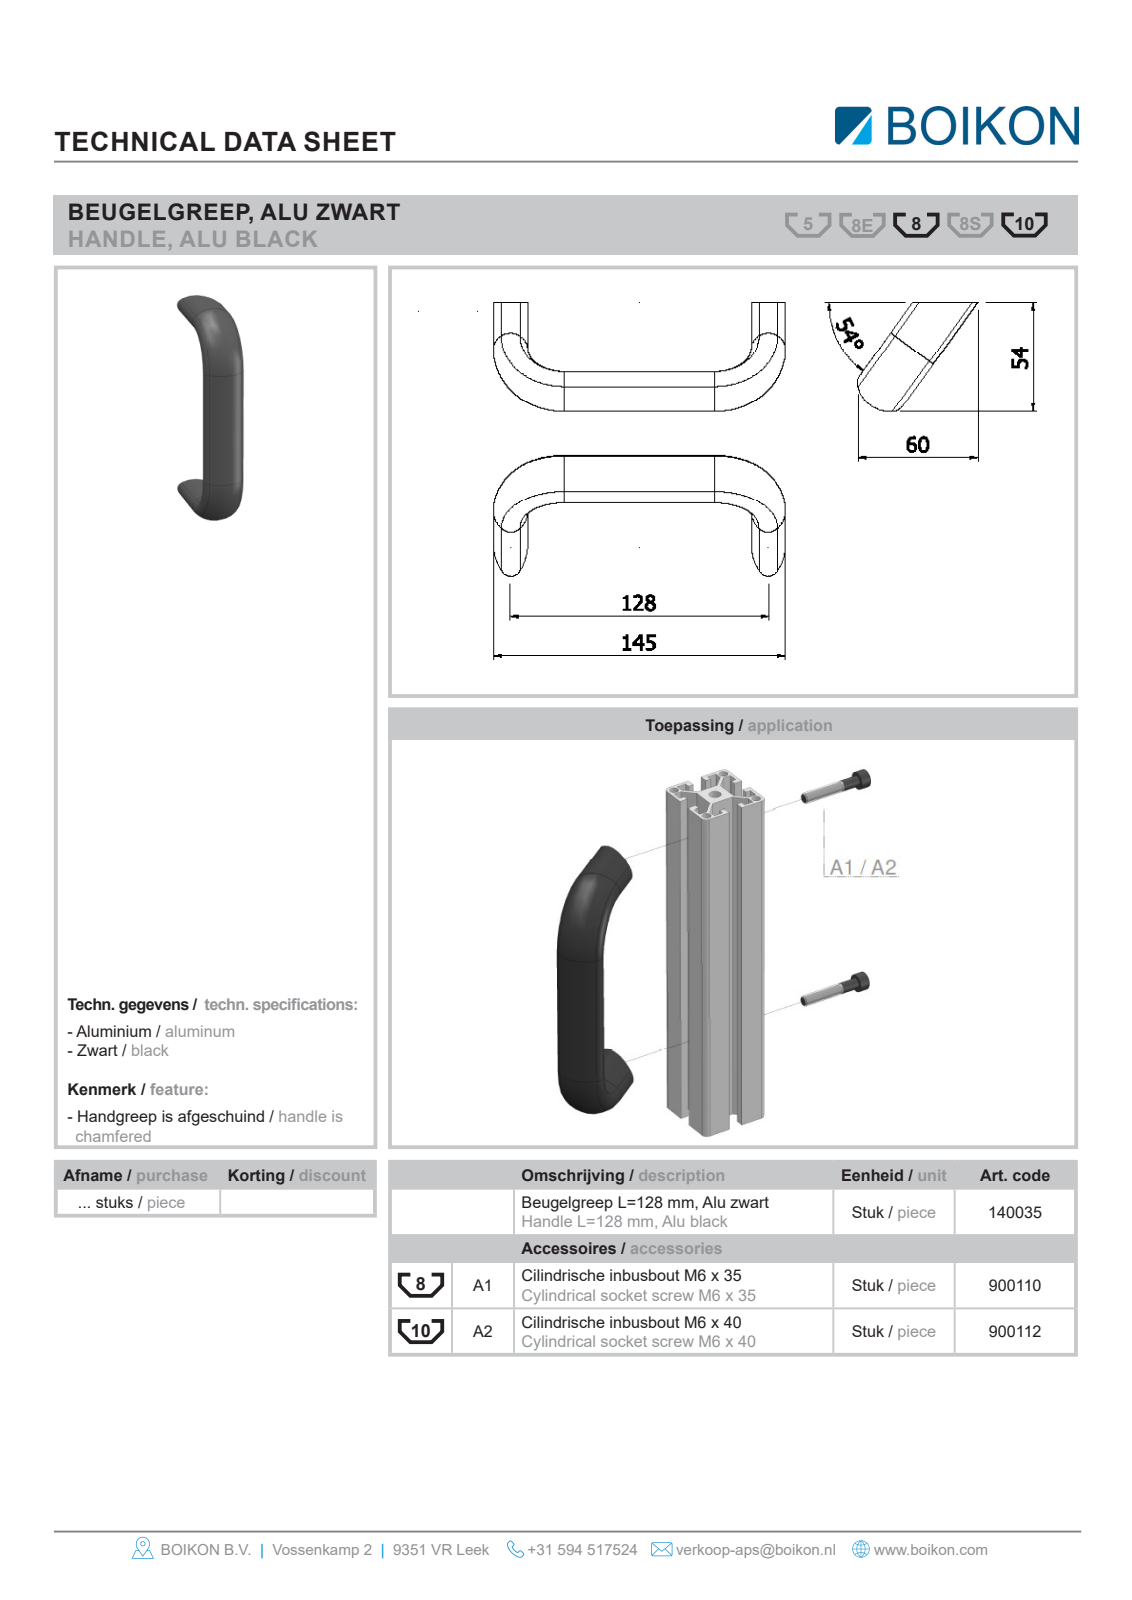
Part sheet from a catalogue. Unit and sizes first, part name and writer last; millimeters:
Units: millimetres
Overall size (bounding box): 145.01 × 87.64 × 59.9
Round holes (diameter × count): ⌀6.65 ×1, ⌀6.65 ×1
Round bosses / shafts (diameter × count): ⌀10 ×2, ⌀6 ×2, ⌀4.77 ×2
Partial cylindrical surfaces — rounded edges, fillets, slot ends (radius × count): R5.67 ×6, R16.49 ×6
Main face-to-face distances: 27.6, 6, 33.6, 5, 41, 35, 7.4, 8.84, 114.94, 106.12
Hole centre spacings: 128
Volume: 74 065 mm³ · Surface area: 17 866 mm²
Bodies: 3 solids, 74 faces (36 planar, 20 cylindrical, 18 other)
Part name (STEP PRODUCT): Root; 140035Beugelgreep L=128 mm, Alu zwartBOIKON; 900110Cil. inbusbout DIN 912 EV M6 x 35BOIKON0
STEP written by: HiCAD 2013 1802.4 Build 509 (AUTOMOTIVE_DESIGN)
